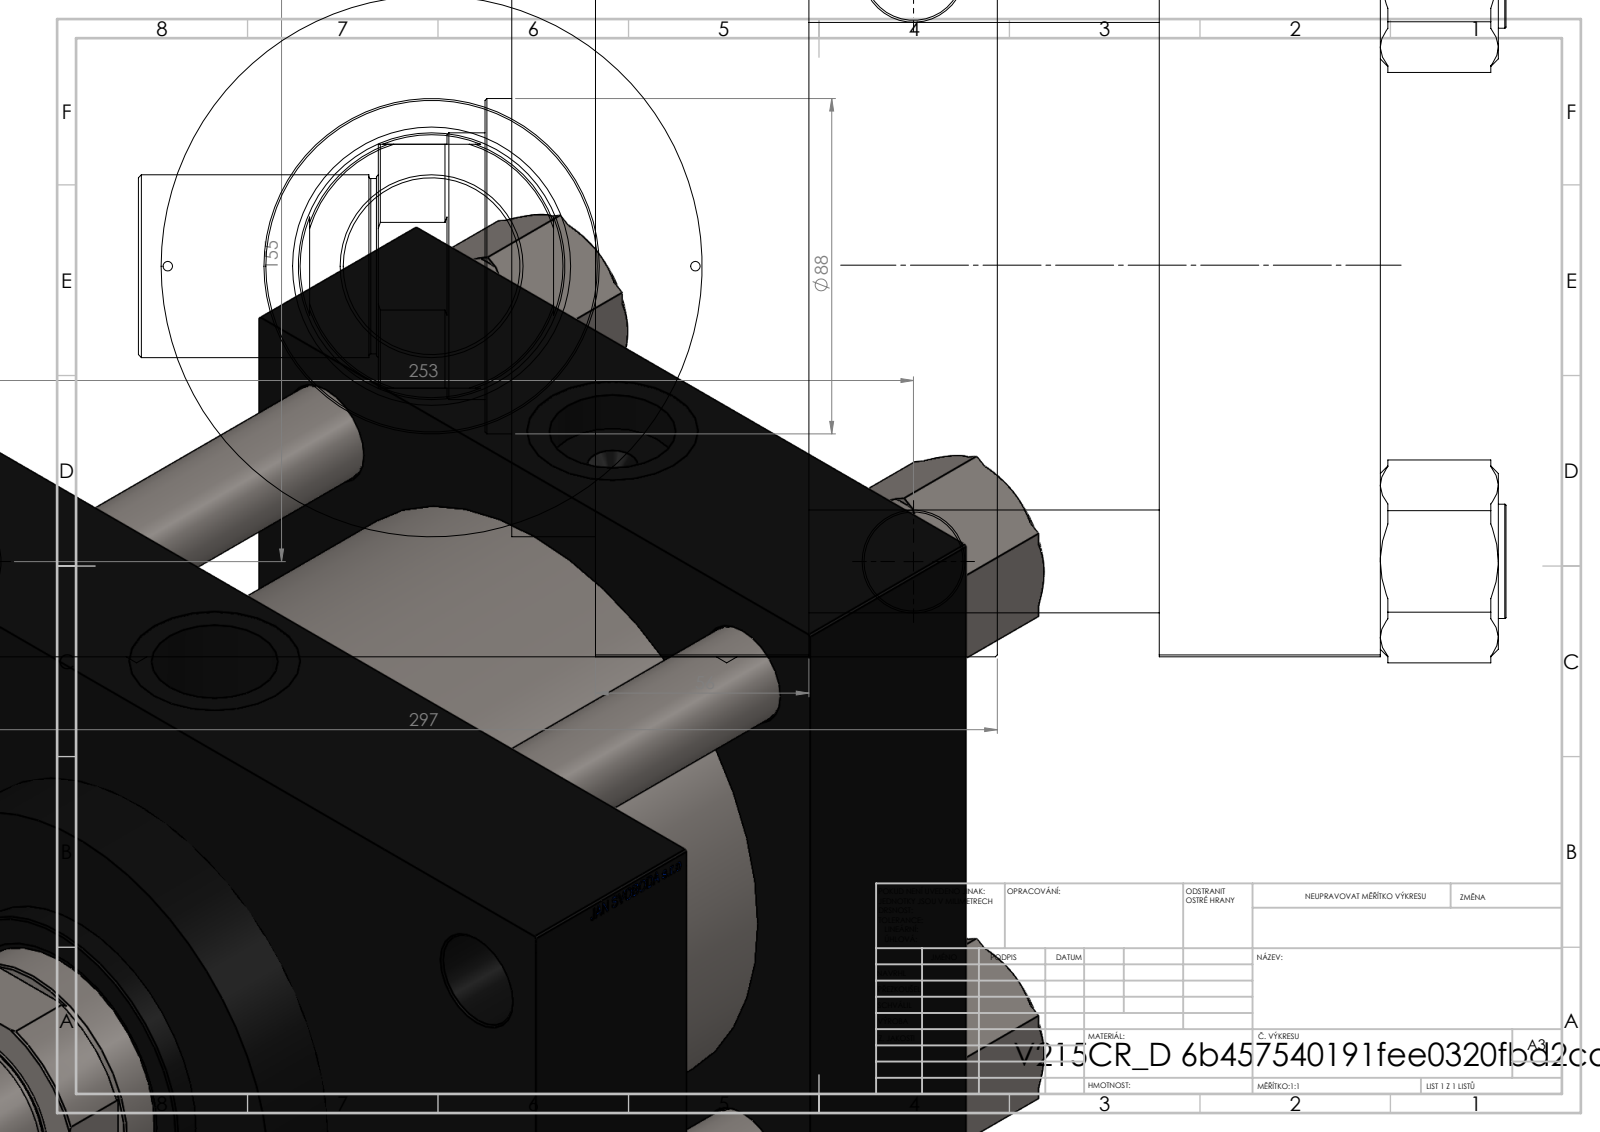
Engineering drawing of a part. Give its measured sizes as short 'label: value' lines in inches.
name: V215CR_VCP_D; V215CR_D_Body; V215_VC_A; NUT_M5_D (+2 more)
written by: SolidWorks 2019 (CONFIG_CONTROL_DESIGN)
unit: in
bodies: 12 solids, 1169 faces (550 planar, 95 cylindrical, 524 other)
size: 14.134 × 11.693 × 8.194
volume: 488.7 in³; area: 1 144 in²
holes: 4× ⌀1.024, 4× ⌀1.063, 2× ⌀0.098, 2× ⌀0.276, 2× ⌀1.309, 2× ⌀1.772, 1× ⌀1.831, 1× ⌀2.756, 1× ⌀2.874, 1× ⌀4.724, 1× ⌀5.591, 1× ⌀6.299
bosses: 4× ⌀1.181, 1× ⌀6.535, 1× ⌀3.465, 1× ⌀1.89, 1× ⌀1.811
rounds: 1× R1.339
face distances: 2.283, 5.906, 3.622, 8.11, 5.827, 2.205, 8.071, 1.811, 9.882, 2.835
hole spacings: 1.931, 3.066, 3.793, 4.312, 5.841, 6.098, 6.399, 6.531
